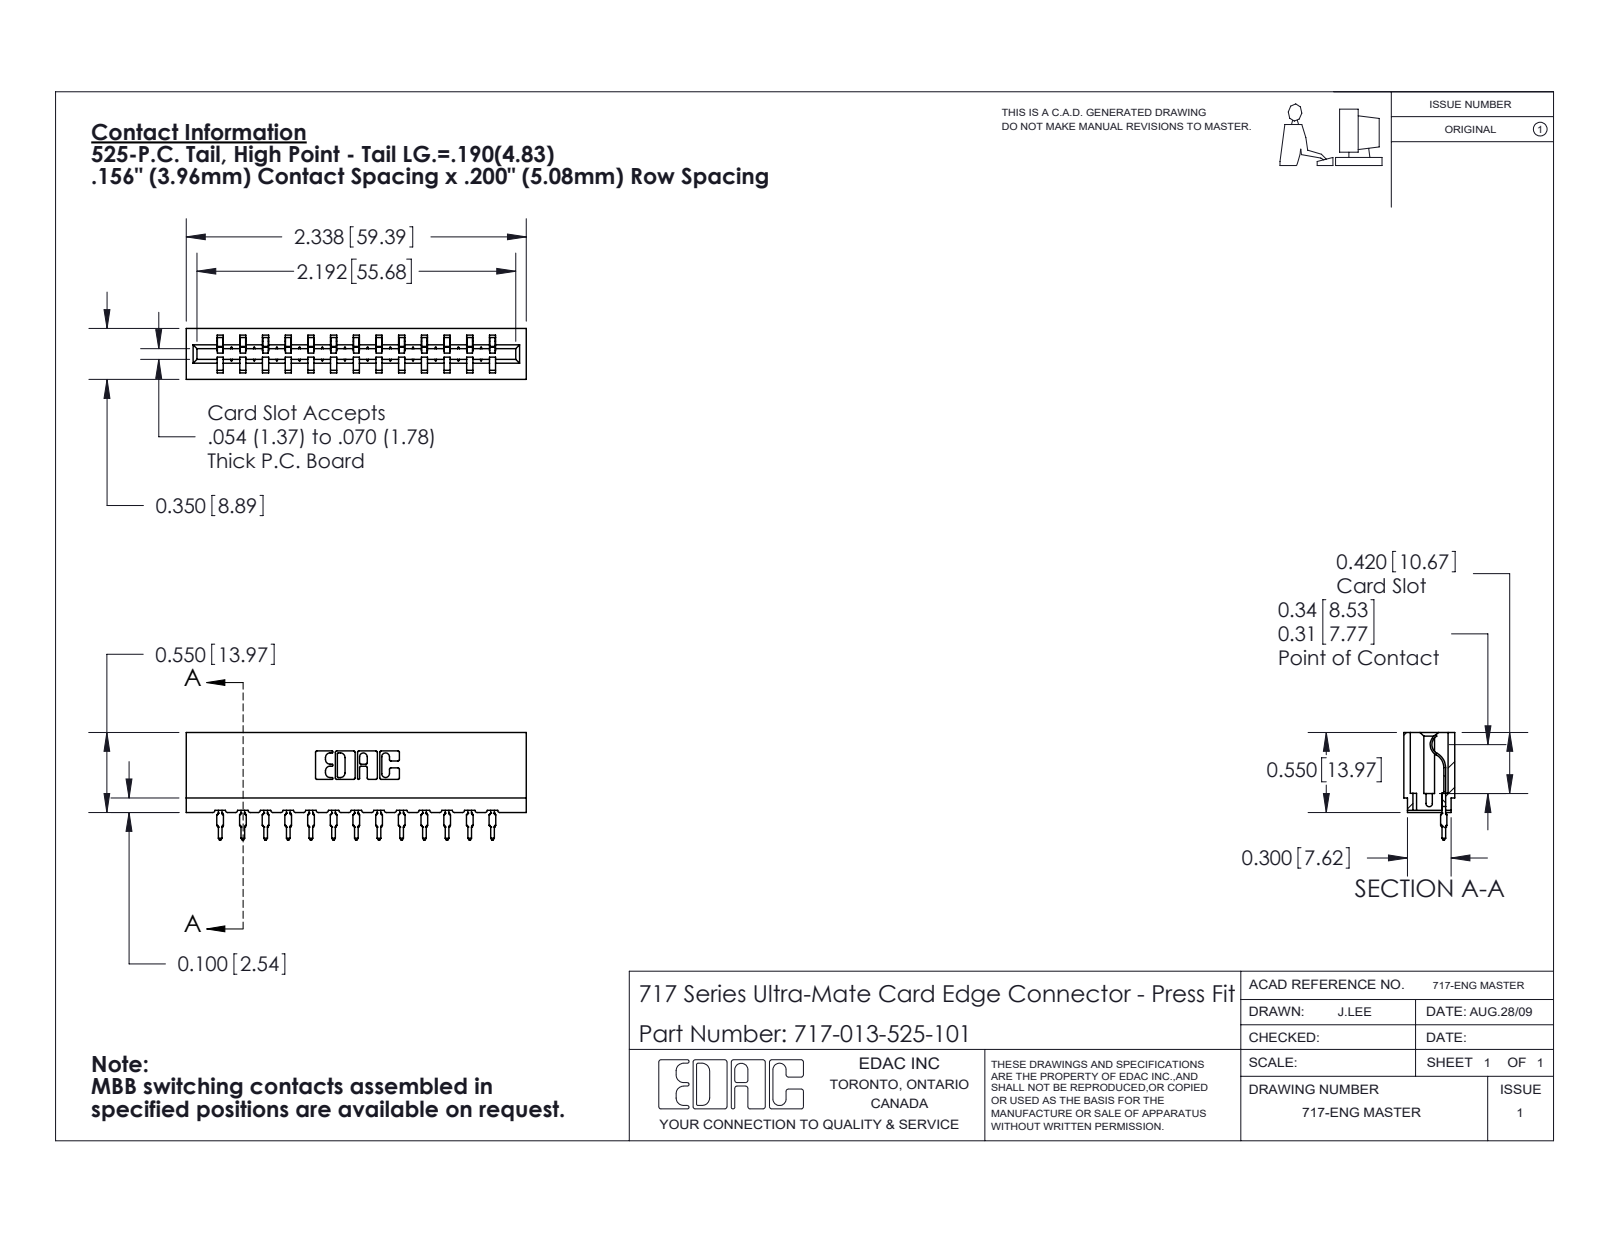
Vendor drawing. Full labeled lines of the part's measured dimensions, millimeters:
Part name (STEP PRODUCT): 717 Part_Insulator Option - 06; 717-013-525-101; 745-292-001_525
STEP written by: SolidWorks 2020 (CONFIG_CONTROL_DESIGN)
Units: millimetres
Bodies: 14 solids, 1563 faces (938 planar, 287 cylindrical, 338 other)
Overall size (bounding box): 59.4 × 18.8 × 8.9
Volume: 5 130 mm³ · Surface area: 6 858 mm²
Partial cylindrical surfaces — rounded edges, fillets, slot ends (radius × count): R0.4 ×26, R0.5 ×26, R0.3 ×22, R0.2 ×6, R0.8 ×6, R0.1 ×4, R0.3 ×4, R0.7 ×3
Main face-to-face distances: 5.4, 3.5, 4, 8.9, 15.8, 11.9, 7.9, 5, 1.9, 1.1
